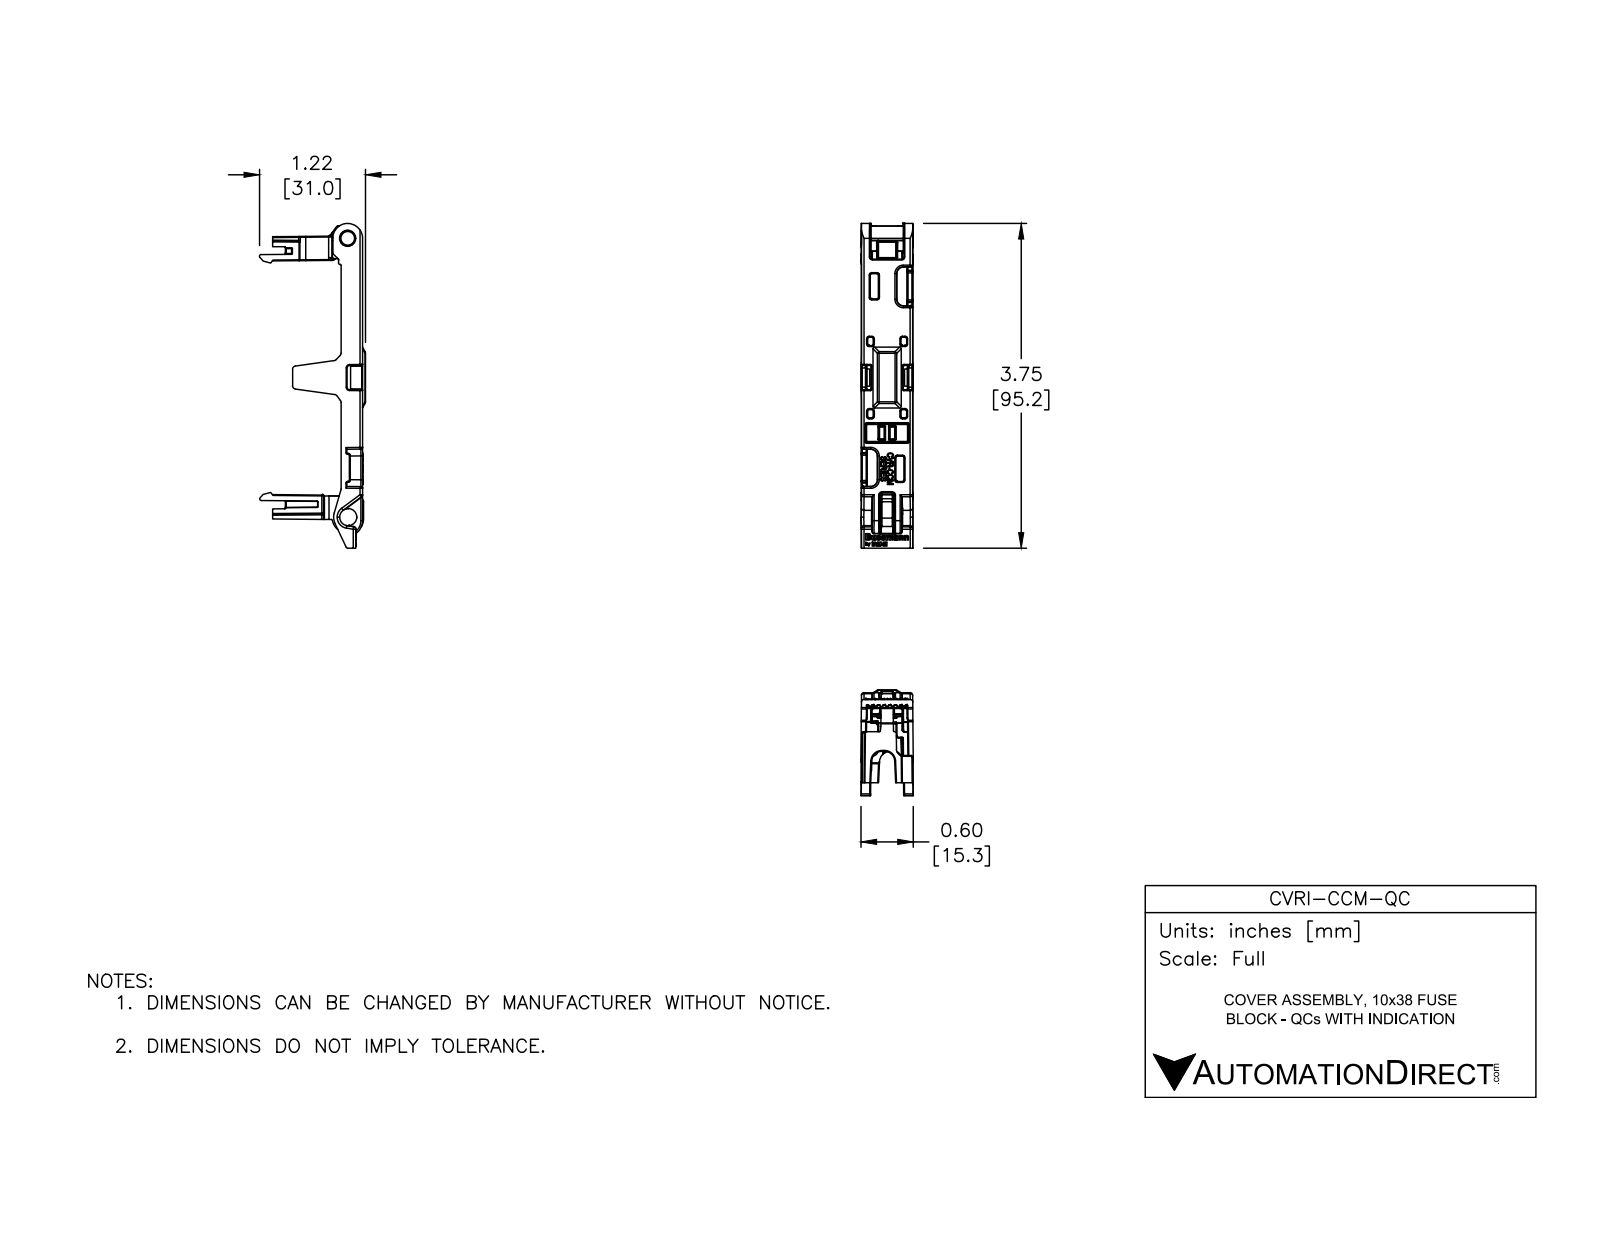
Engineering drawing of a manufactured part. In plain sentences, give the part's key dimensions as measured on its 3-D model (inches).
The part is named "CVRI-CCM-QC". Its 3-D file was written by "SolidWorks 2016 (AUTOMOTIVE_DESIGN)". It is 3 solids with 2408 faces: 631 planar, 863 cylindrical and 914 other. Overall it measures 3.748 by 1.222 by 0.605 inches. Its volume is 0.395 cubic inches and its surface area 13.67 square inches. Round holes: 1 of diameter 0.157, 1 of diameter 0.185, 1 of diameter 0.197. Round bosses or shafts: 1 of diameter 0.177, 1 of diameter 0.15. Partial cylindrical surfaces (rounded edges, fillets, slot ends): 261 of radius 0.01, 154 of radius 0.006, 147 of radius 0.004, 66 of radius 0.02, 18 of radius 0.03, 17 of radius 0.039, 7 of radius 0.067, 4 of radius 0.079. The main face-to-face distances are 0.061, 0.061, 0.247, 0.186, 0.185, 0.114, 0.08, 0.222, 0.281, 0.382. The hole center spacings are 3.219.
